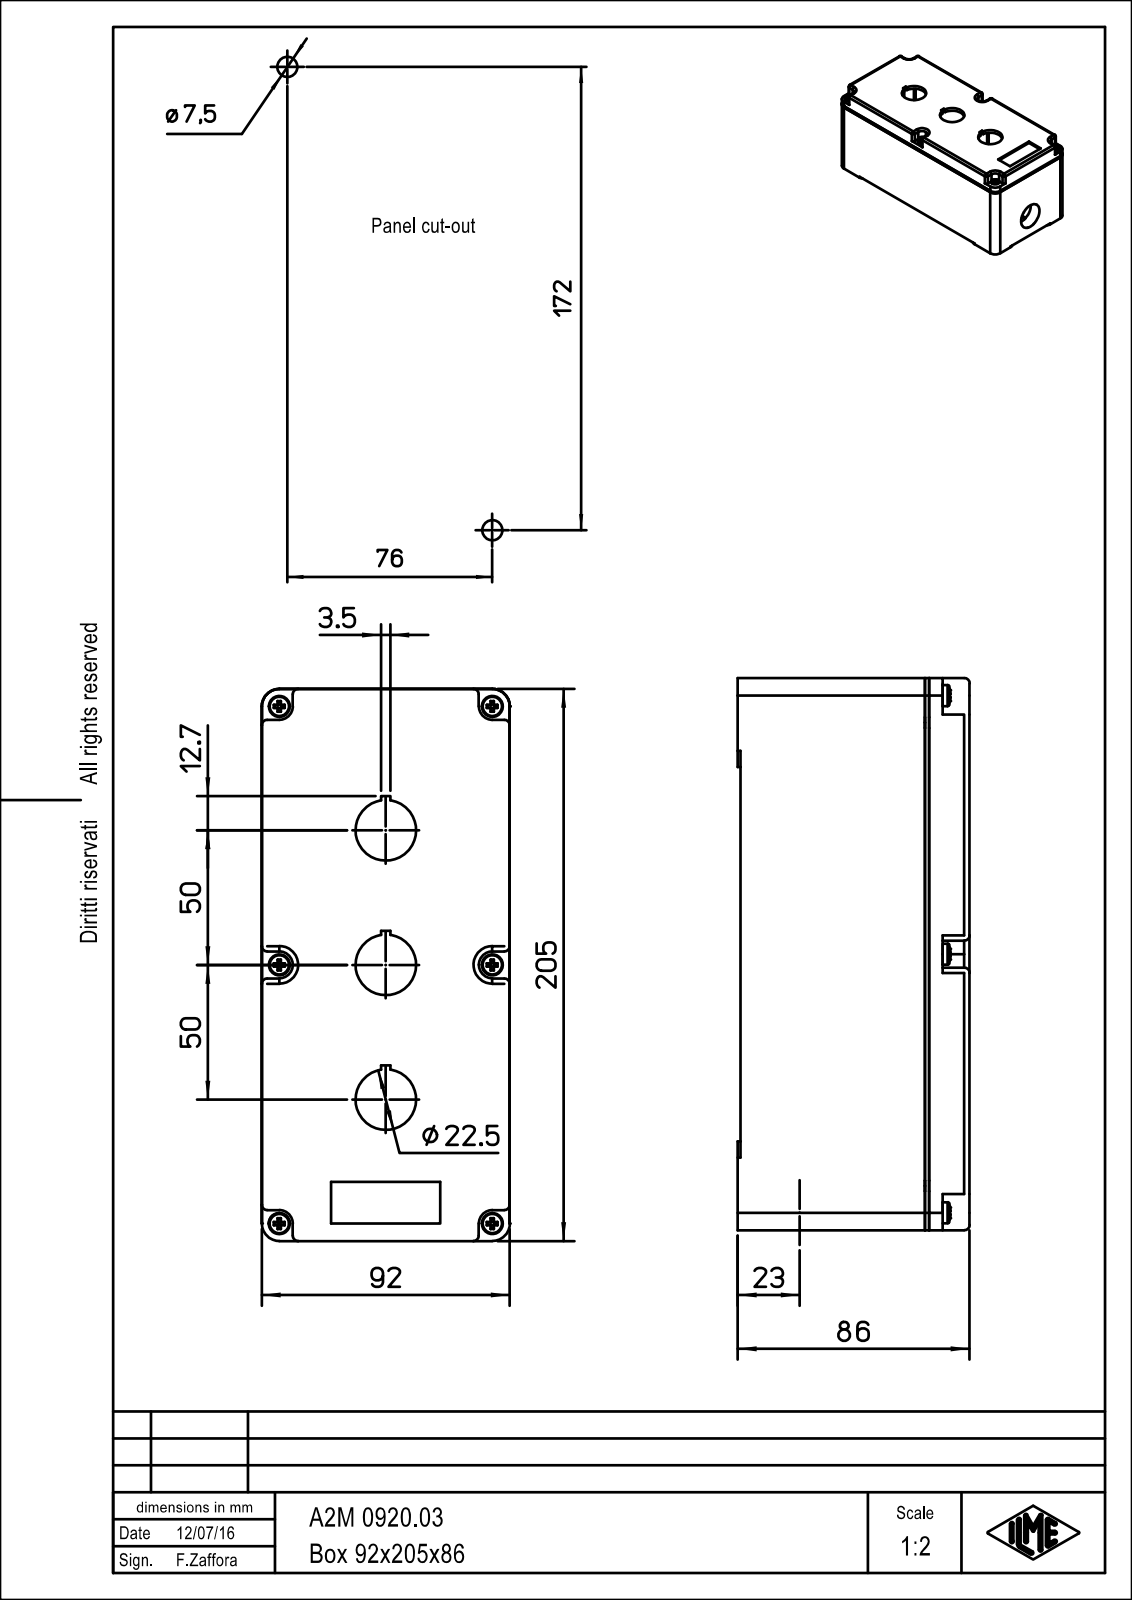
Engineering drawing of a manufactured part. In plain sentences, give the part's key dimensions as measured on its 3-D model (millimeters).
The part is named "COPERCHIO_C_0920.03; CASSETTA_B_0920; GUARNIZIONE_0920; VITE_M4X20 (+2 more)". Its 3-D file was written by "Creo Elements/Direct Modeling 17.0C 05-Feb-2011 (C) Parametric Technology GmbH (AUTOMOTIVE_DESIGN)". It is 11 solids with 1183 faces: 862 planar, 267 cylindrical and 54 other. Overall it measures 205 by 92 by 86 millimeters. Its volume is 355 829 cubic millimeters and its surface area 199 550 square millimeters. Round holes: 8 of diameter 3.3, 8 of diameter 3.8, 6 of diameter 4.5, 6 of diameter 5, 6 of diameter 6, 3 of diameter 22.5, 2 of diameter 5.8, 2 of diameter 7.5, 1 of diameter 10.6, 1 of diameter 10.61, 1 of diameter 25.4. Round bosses or shafts: 9 of diameter 4, 6 of diameter 7.8, 6 of diameter 3.5, 2 of diameter 6.2, 2 of diameter 6, 1 of diameter 7. Partial cylindrical surfaces (rounded edges, fillets, slot ends): 22 of radius 0.33, 22 of radius 2, 12 of radius 6, 8 of radius 5, 8 of radius 6.5, 8 of radius 8, 4 of radius 0.27, 4 of radius 0.27. The main face-to-face distances are 3, 82, 92, 85, 79, 4.38, 4.37, 83.25, 1.5, 87.62. The hole center spacings are 79, 124.33, 96, 39.5, 60.63, 63.72, 78.14, 95.99.
